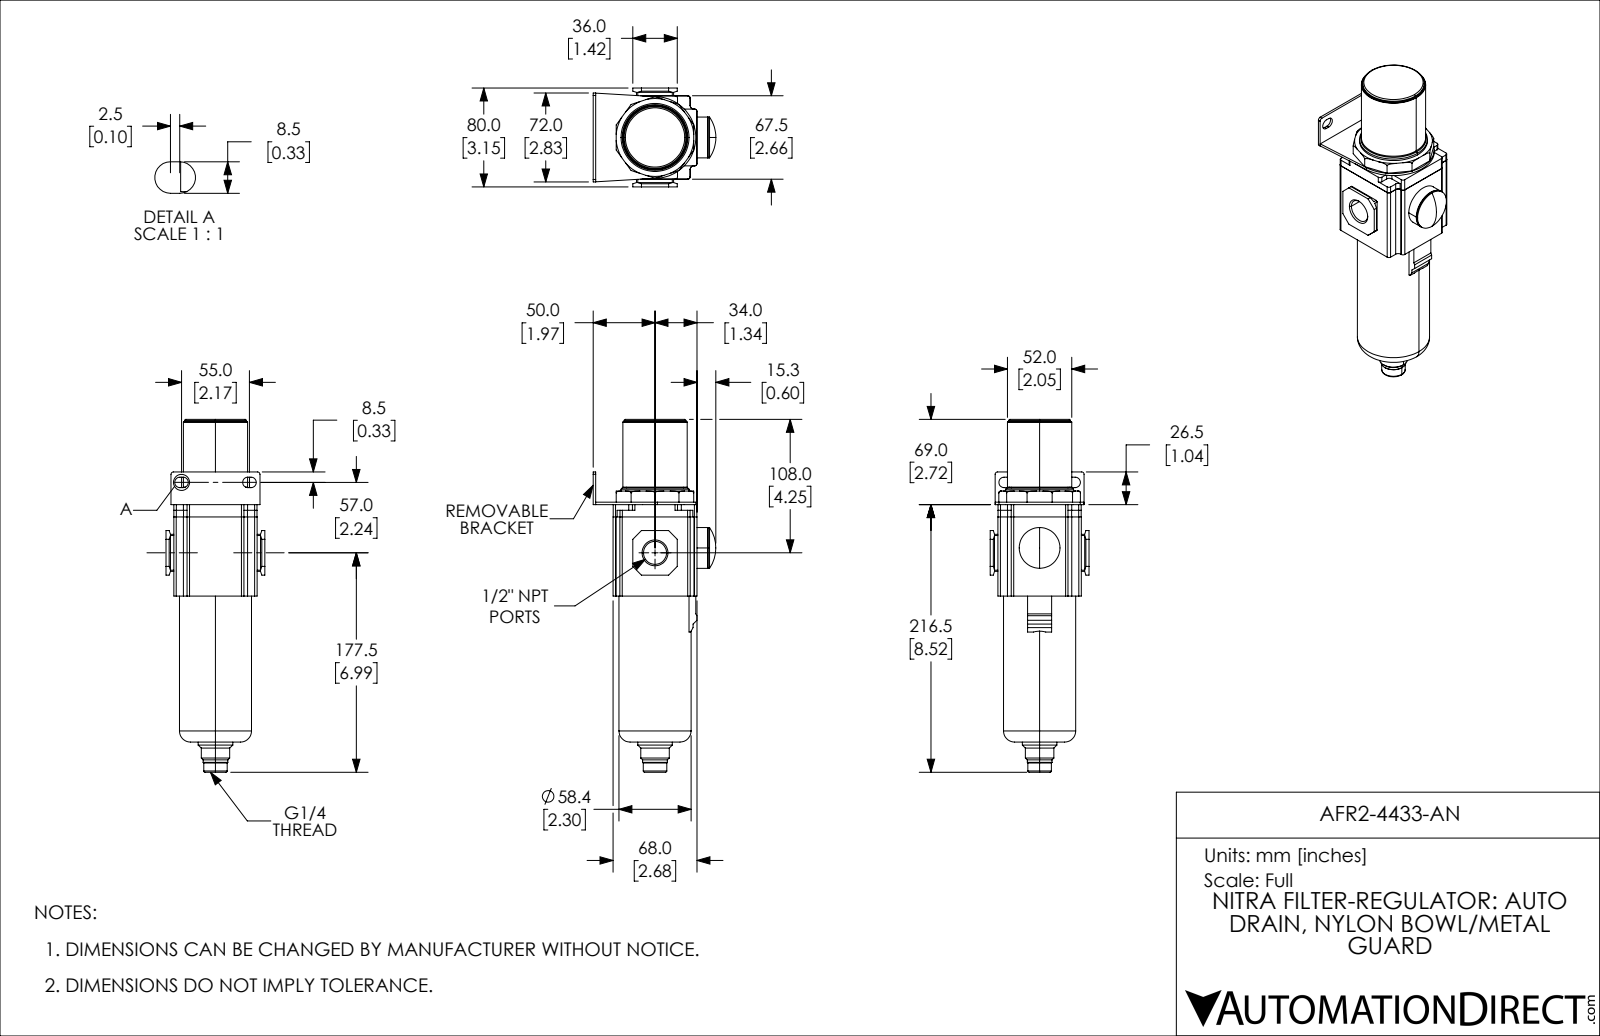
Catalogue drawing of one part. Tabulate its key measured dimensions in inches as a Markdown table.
| quantity | value |
| --- | --- |
| part name | AFR2-4433-AN |
| STEP written by | SolidWorks 2019 (CONFIG_CONTROL_DESIGN) |
| units | inches |
| bodies | 1 solid, 222 faces (119 planar, 67 cylindrical, 36 other) |
| overall size | 11.24 × 3.909 × 3.15 |
| volume | 50.17 in³ |
| surface area | 117.8 in² |
| round holes (diameter × count) | 0.451 × 1, 0.733 × 1 |
| round bosses / shafts (diameter × count) | 2.299 × 1, 2.165 × 1, 2.047 × 1, 1.969 × 1, 1.807 × 1, 1.299 × 1, 1.102 × 1, 0.906 × 1 |
| partial cylindrical surfaces (radius × count) | 0.079 × 22, 0.118 × 12, 0.167 × 4, 1.299 × 1 |
| main face-to-face distances | 0.079, 2.657, 2.638, 2.677, 0.63, 2.717, 3.307, 0.246, 2.904, 2.992 |
